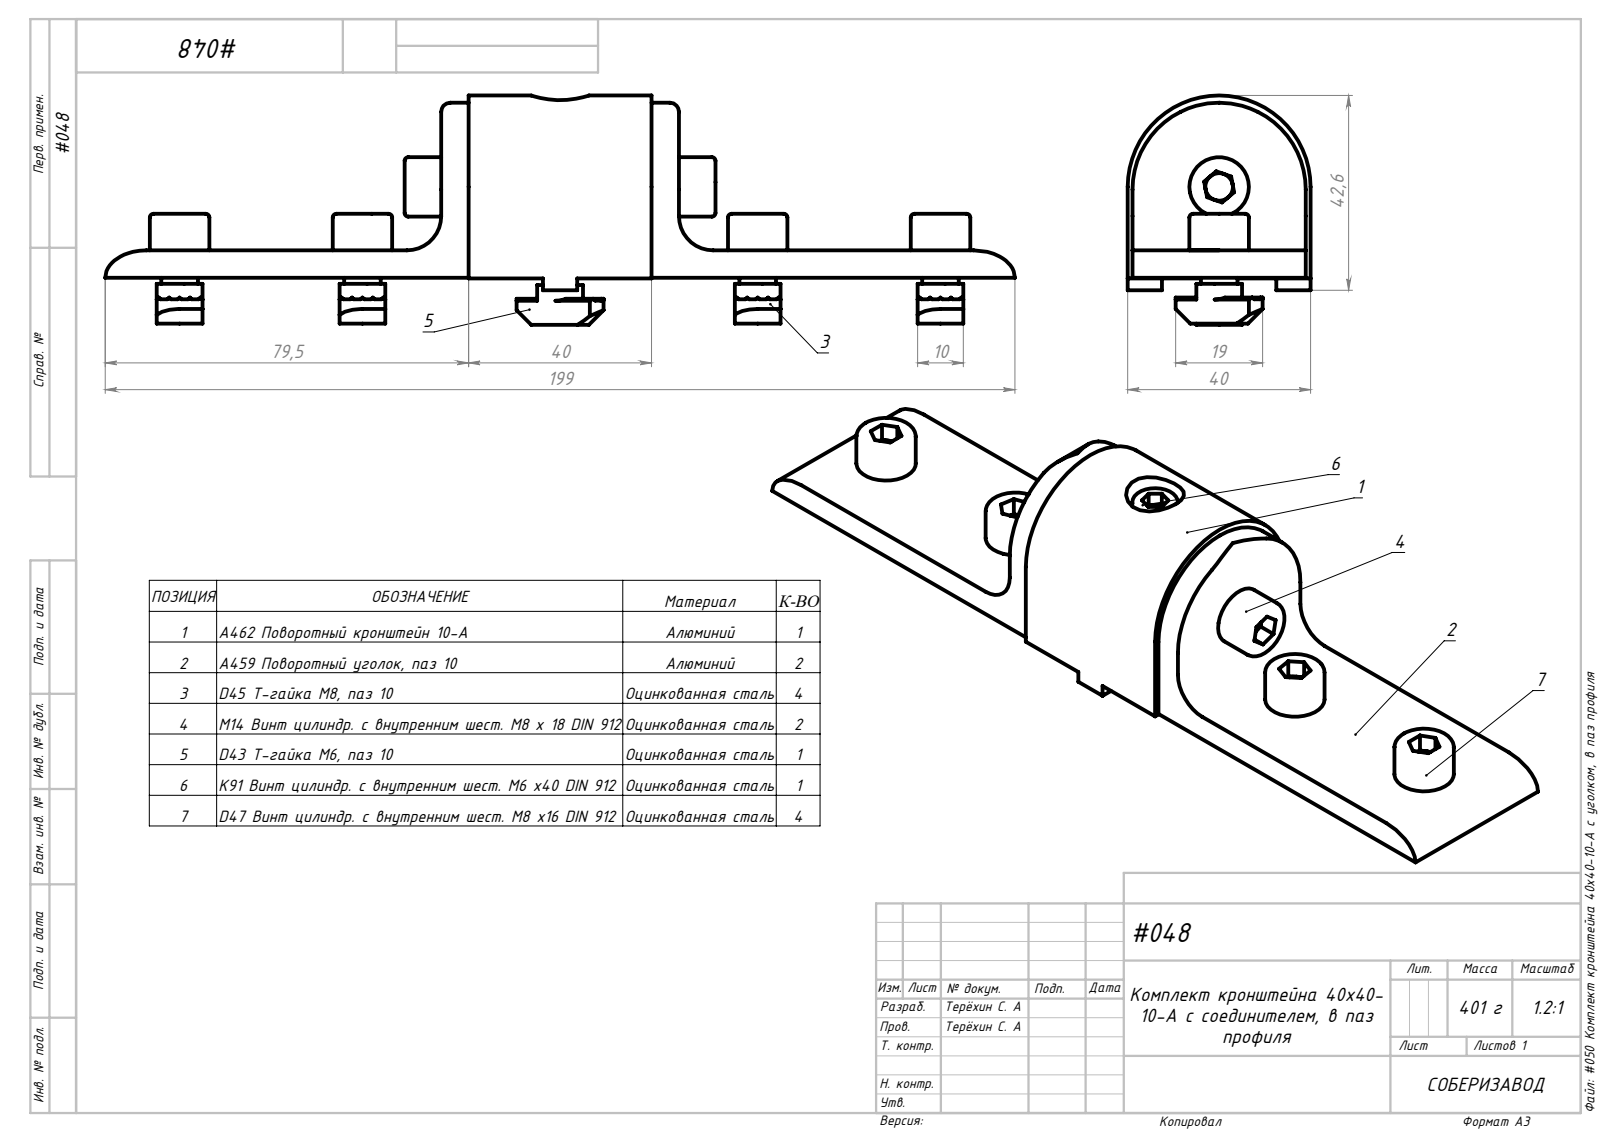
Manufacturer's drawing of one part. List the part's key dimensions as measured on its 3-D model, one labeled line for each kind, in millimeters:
Part name (STEP PRODUCT): M14 Винт цилиндр. с внутренним шест. М8 х 18 DIN 912; D45 Т-гайка М8, паз 10_00; A459 Поворотный уголок, паз 10; D43 Т-гайка М6, паз 10_00 (+4 more)
STEP written by: SolidWorks 2021 (AUTOMOTIVE_DESIGN)
Units: millimetres
Bodies: 15 solids, 500 faces (321 planar, 87 cylindrical, 92 other)
Overall size (bounding box): 199 × 50.15 × 40
Volume: 116 969 mm³ · Surface area: 41 517 mm²
Round holes (diameter × count): ⌀8.35 ×5, ⌀6.7 ×4, ⌀5 ×1, ⌀6.5 ×1, ⌀8.5 ×1, ⌀12.7 ×1
Round bosses / shafts (diameter × count): ⌀13 ×5, ⌀8 ×5, ⌀10 ×1, ⌀6 ×1
Partial cylindrical surfaces — rounded edges, fillets, slot ends (radius × count): R5.67 ×10, R6 ×10, R2 ×2, R7.5 ×2, R19 ×2, R20 ×1
Main face-to-face distances: 6, 40, 1.05, 38.95, 46, 6.13, 37.9, 10, 52, 16
Hole centre spacings: 40, 126.45, 39.99, 40.01, 43.22, 43.23, 83.22, 83.23
